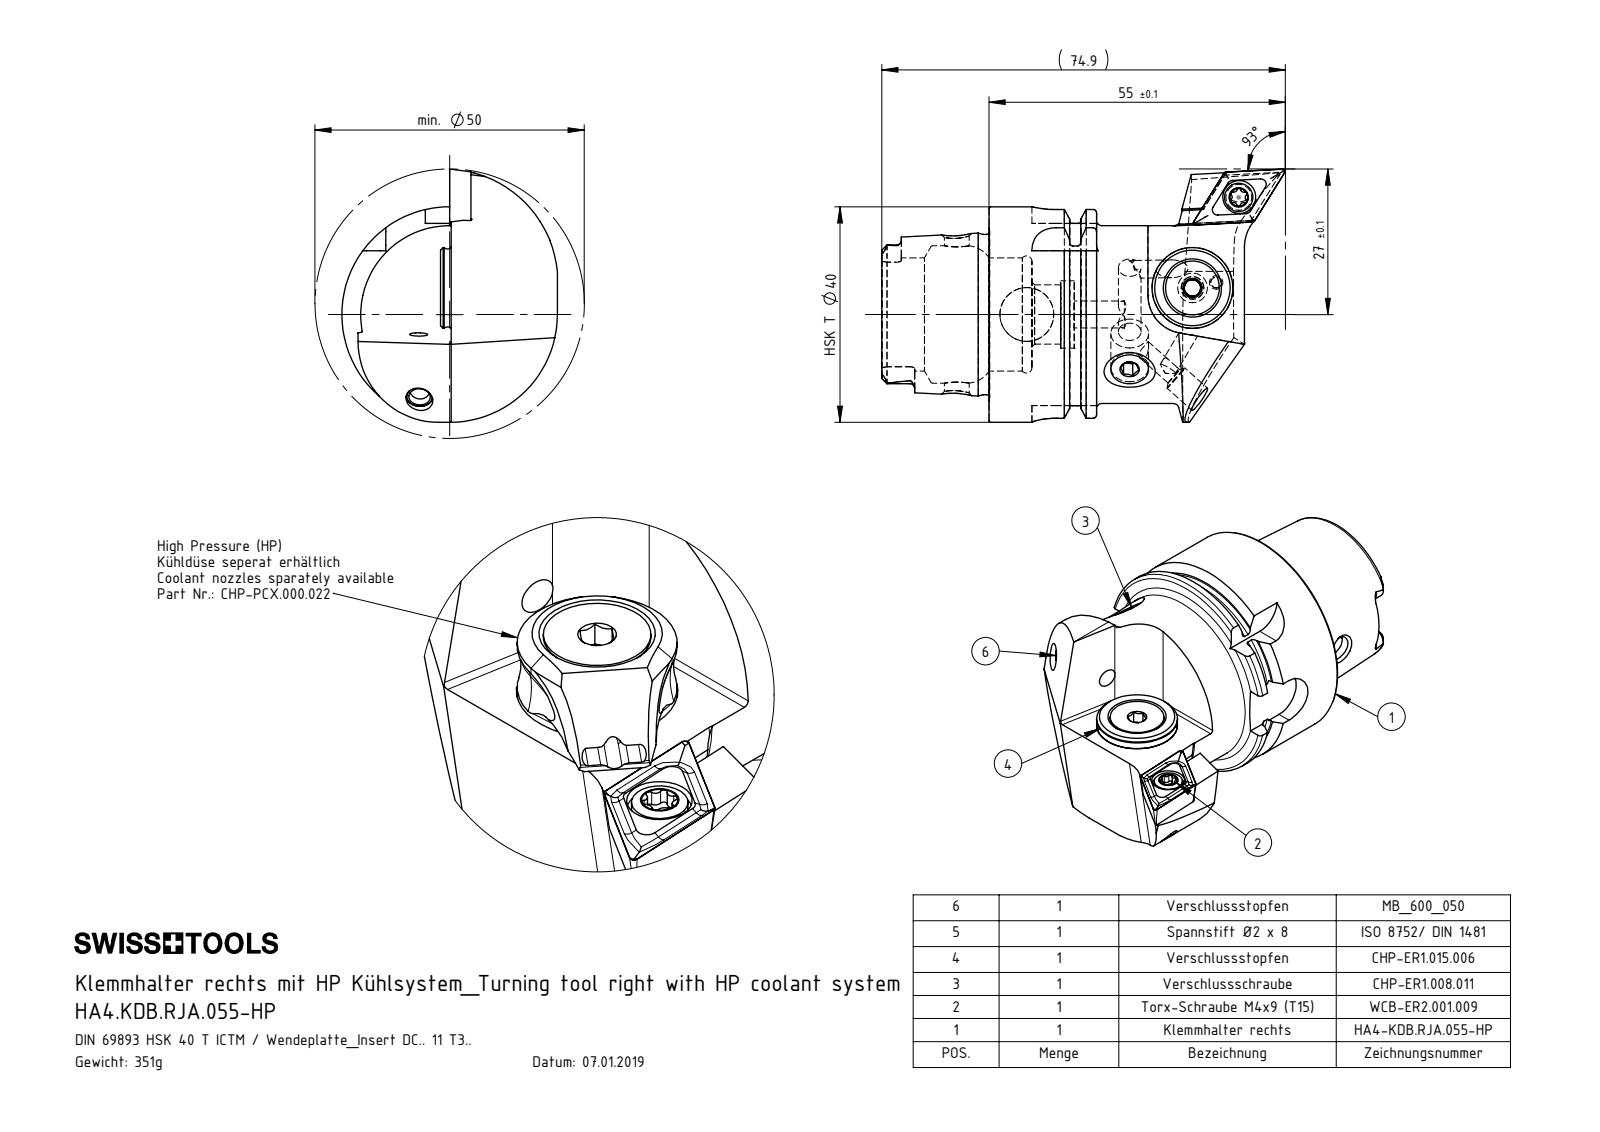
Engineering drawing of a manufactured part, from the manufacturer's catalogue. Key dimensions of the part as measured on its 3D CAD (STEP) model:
Part name (STEP PRODUCT): DIN 7991 - M5x15; DIN 3771 - 13x1; CHP-ER1.008.011_A; DCMT11T304 (+7 more)
STEP written by: SolidWorks 2017 (AUTOMOTIVE_DESIGN)
Units: millimetres
Bodies: 10 solids, 461 faces (123 planar, 129 cylindrical, 209 other)
Overall size (bounding box): 74.91 × 47 × 40
Volume: 44 407 mm³ · Surface area: 16 999 mm²
Round holes (diameter × count): ⌀3.3 ×4, ⌀4.2 ×2, ⌀5 ×2, ⌀1.2 ×1, ⌀2 ×1, ⌀2.5 ×1, ⌀3 ×1, ⌀4 ×1, ⌀4.4 ×1, ⌀4.6 ×1, ⌀5.2 ×1, ⌀6.1 ×1
Round bosses / shafts (diameter × count): ⌀5 ×2, ⌀40 ×1, ⌀34.75 ×1, ⌀33 ×1, ⌀29.71 ×1, ⌀15 ×1, ⌀13.4 ×1, ⌀10 ×1
Partial cylindrical surfaces — rounded edges, fillets, slot ends (radius × count): R0.34 ×6, R0.59 ×6, R0.9 ×6, R4.5 ×4, R0.5 ×2, R1.82 ×2, R1.88 ×2, R7 ×2
Main face-to-face distances: 4.5, 7.95, 19.95, 12, 0.83, 3.67, 29.5, 21.55, 9.55, 19.9
Hole centre spacings: 4.5, 16.34, 16.43, 18.87, 18.97, 31.15, 35.65, 44.96
